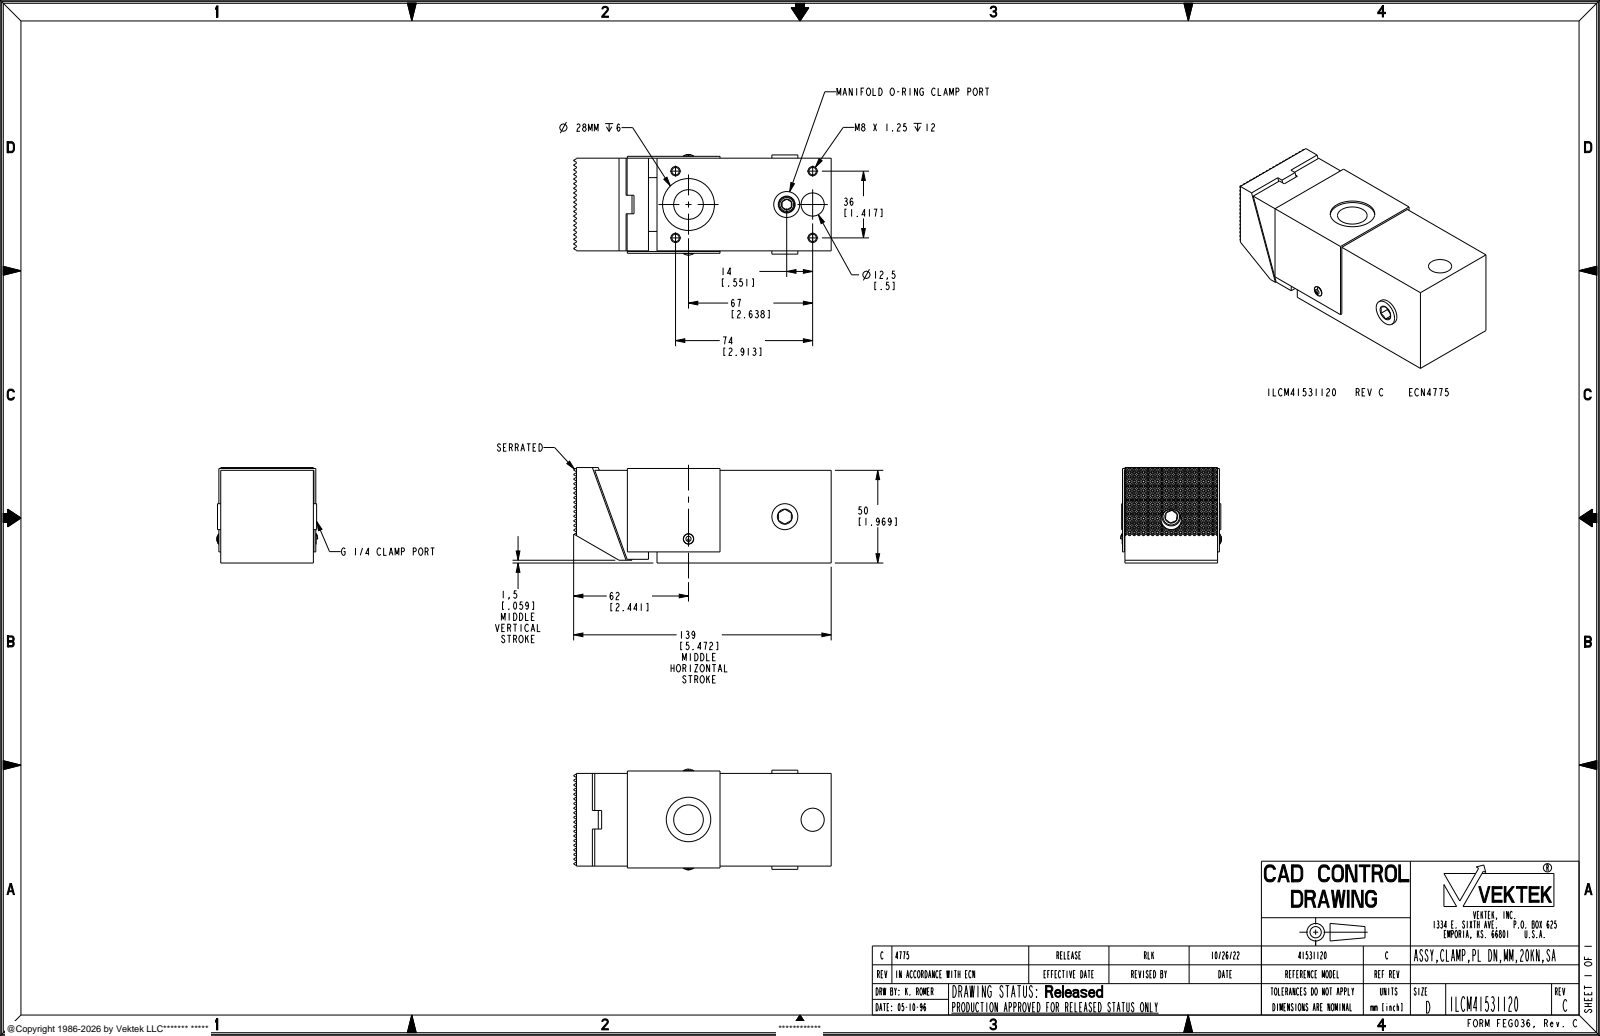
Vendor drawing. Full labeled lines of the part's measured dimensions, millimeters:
Part name (STEP PRODUCT): ILCM41531120
STEP written by: CREO PARAMETRIC BY PTC INC, 2021164 (AUTOMOTIVE_DESIGN)
Units: millimetres
Bodies: 5 solids, 1789 faces (1503 planar, 75 cylindrical, 211 other)
Overall size (bounding box): 139 × 54.3 × 51.5
Volume: 99 744 mm³ · Surface area: 73 241 mm²
Round holes (diameter × count): ⌀4 ×4, ⌀5 ×2, ⌀14 ×2, ⌀26 ×2, ⌀3.4 ×1, ⌀6.2 ×1, ⌀9.1 ×1, ⌀11 ×1, ⌀11.45 ×1, ⌀12.5 ×1, ⌀16 ×1, ⌀24 ×1
Round bosses / shafts (diameter × count): ⌀24 ×1, ⌀14 ×1, ⌀10 ×1, ⌀9.73 ×1, ⌀8.5 ×1, ⌀6 ×1, ⌀3 ×1
Partial cylindrical surfaces — rounded edges, fillets, slot ends (radius × count): R8.4 ×2
Main face-to-face distances: 50, 1, 51, 51.3, 1.3, 52.3, 50.3, 4.33, 4.61, 94
Hole centre spacings: 18, 19.31, 22.8, 36, 53, 62.64, 67, 69.38
